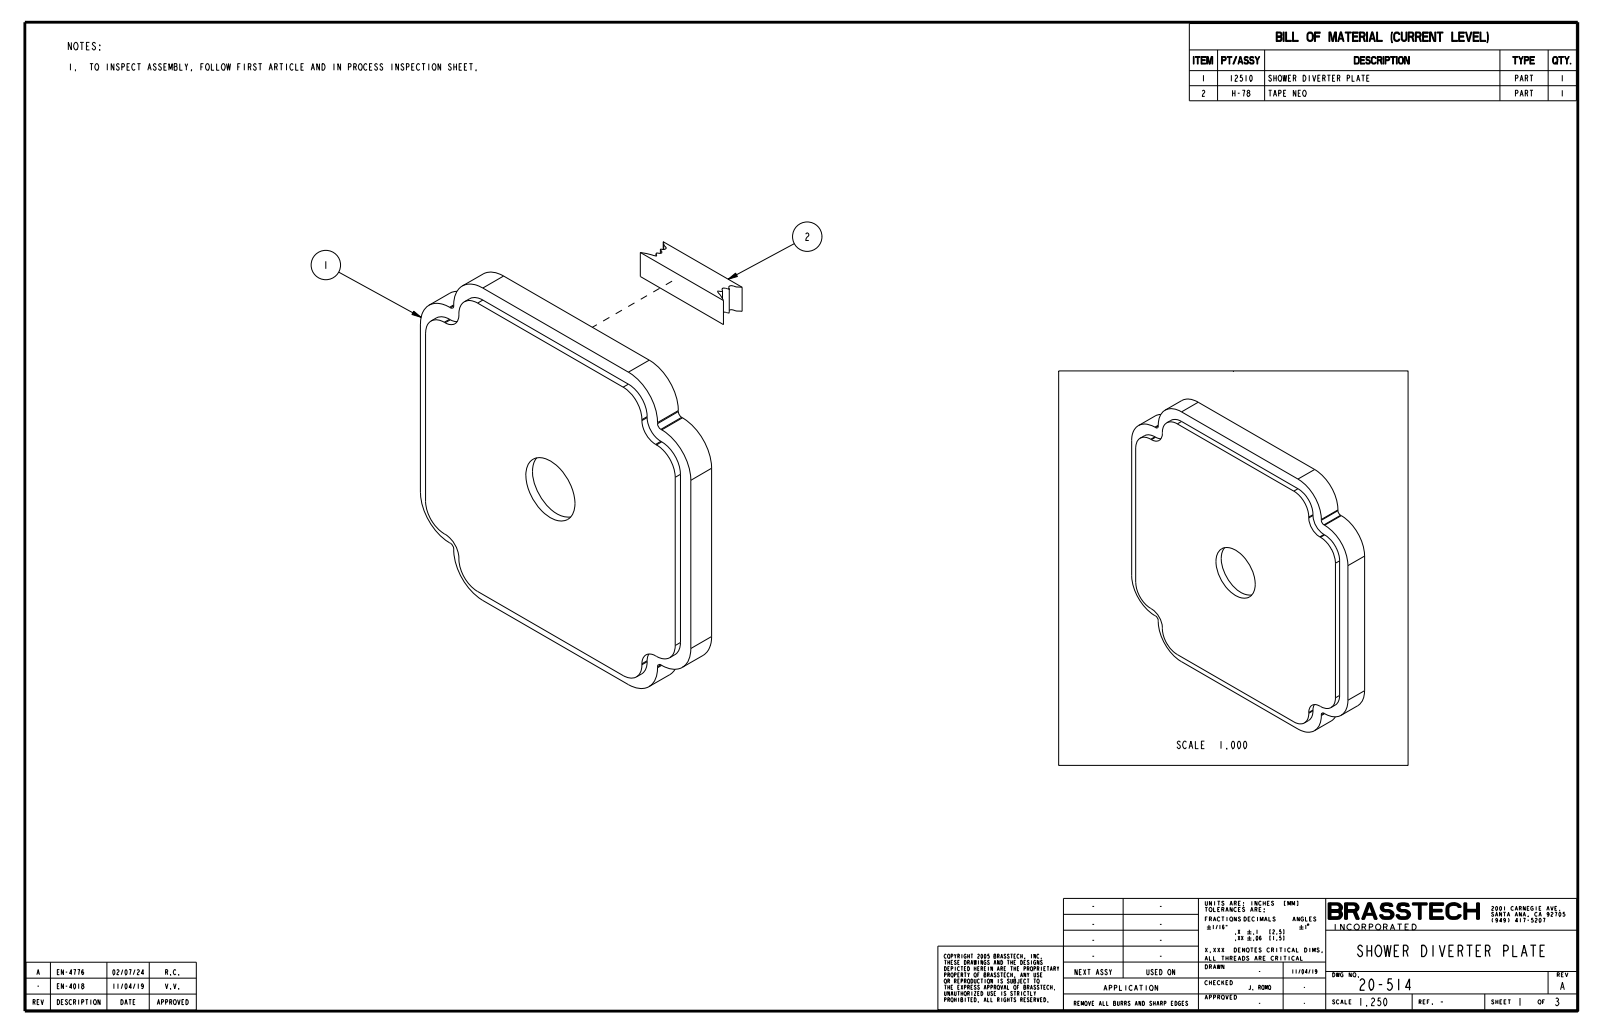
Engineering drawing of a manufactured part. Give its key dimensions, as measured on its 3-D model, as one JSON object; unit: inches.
{"part_name": "12510; 20-514_ASM", "step_written_by": "CREO PARAMETRIC BY PTC INC, 2023134 (CONFIG_CONTROL_DESIGN)", "units": "inches", "bodies": {"solids": 1, "faces": 151, "planar": 53, "cylindrical": 74, "other": 24}, "overall_size": [3.25, 3.25, 0.313], "volume_in3": 0.993, "surface_area_in2": 25.08, "round_holes": [[0.59, 1]], "partial_cylinders_radius": [[0.013, 16], [0.02, 8], [0.225, 8], [0.27, 8], [0.35, 8], [0.04, 4], [0.12, 4], [0.165, 4]], "face_to_face_distances": [0.08, 0.043, 0.123, 0.06, 0.017, 0.063, 3.17, 0.25, 0.19, 0.233]}
